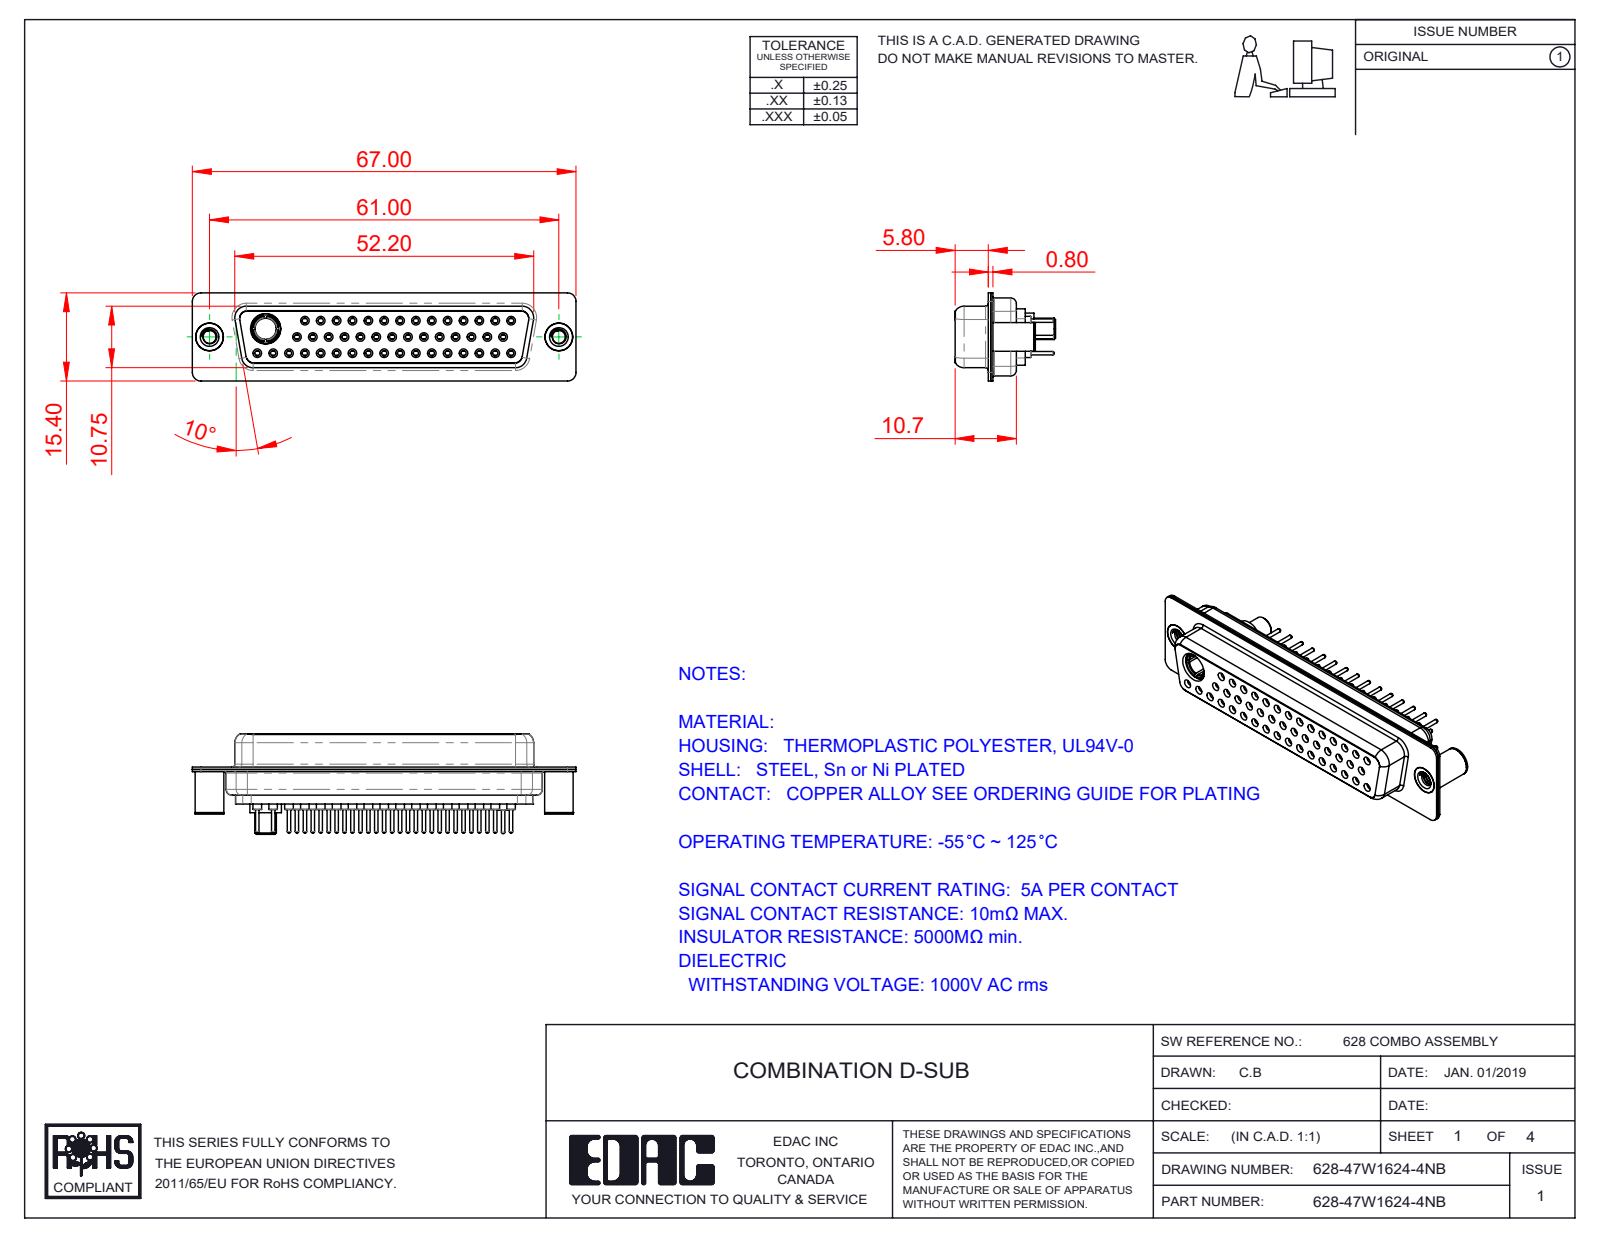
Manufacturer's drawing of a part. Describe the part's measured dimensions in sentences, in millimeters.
The part is named "628Combo Threaded Board Spacer_B; 628Combo Contact Row 3_24; 628Combo Contact Row 1_24; 628Combo Shell Front_50 Contacts (+5 more)". Its 3-D file was written by "SolidWorks 2016 (CONFIG_CONTROL_DESIGN)". It is 53 solids with 2913 faces: 783 planar, 1058 cylindrical and 1072 other. Overall it measures 67 by 17.55 by 15.4 millimeters. Its volume is 7 230 cubic millimeters and its surface area 14 955 square millimeters. Round holes: 46 of diameter 1.1, 45 of diameter 0.9, 45 of diameter 1.5, 45 of diameter 2, 31 of diameter 1.6, 14 of diameter 1.7, 3 of diameter 4.85, 2 of diameter 2.26, 2 of diameter 3.26, 2 of diameter 4, 2 of diameter 4.05, 1 of diameter 3.7. Round bosses or shafts: 46 of diameter 2.2, 46 of diameter 0.6, 15 of diameter 1.6, 2 of diameter 5, 2 of diameter 4.95, 2 of diameter 4.8, 1 of diameter 5.5, 1 of diameter 5.2. Partial cylindrical surfaces (rounded edges, fillets, slot ends): 16 of radius 1.5, 12 of radius 1.35, 12 of radius 2, 8 of radius 1.6, 4 of radius 0.25, 4 of radius 0.5, 4 of radius 0.6, 4 of radius 0.65. The main face-to-face distances are 0.4, 11.33, 6.45, 6.05, 1.87, 12.25, 6.2, 5.8, 10.35, 10.93. The hole center spacings are 3.16, 2.77, 5.54, 8.31, 11.08, 13.85, 16.62, 19.39.
